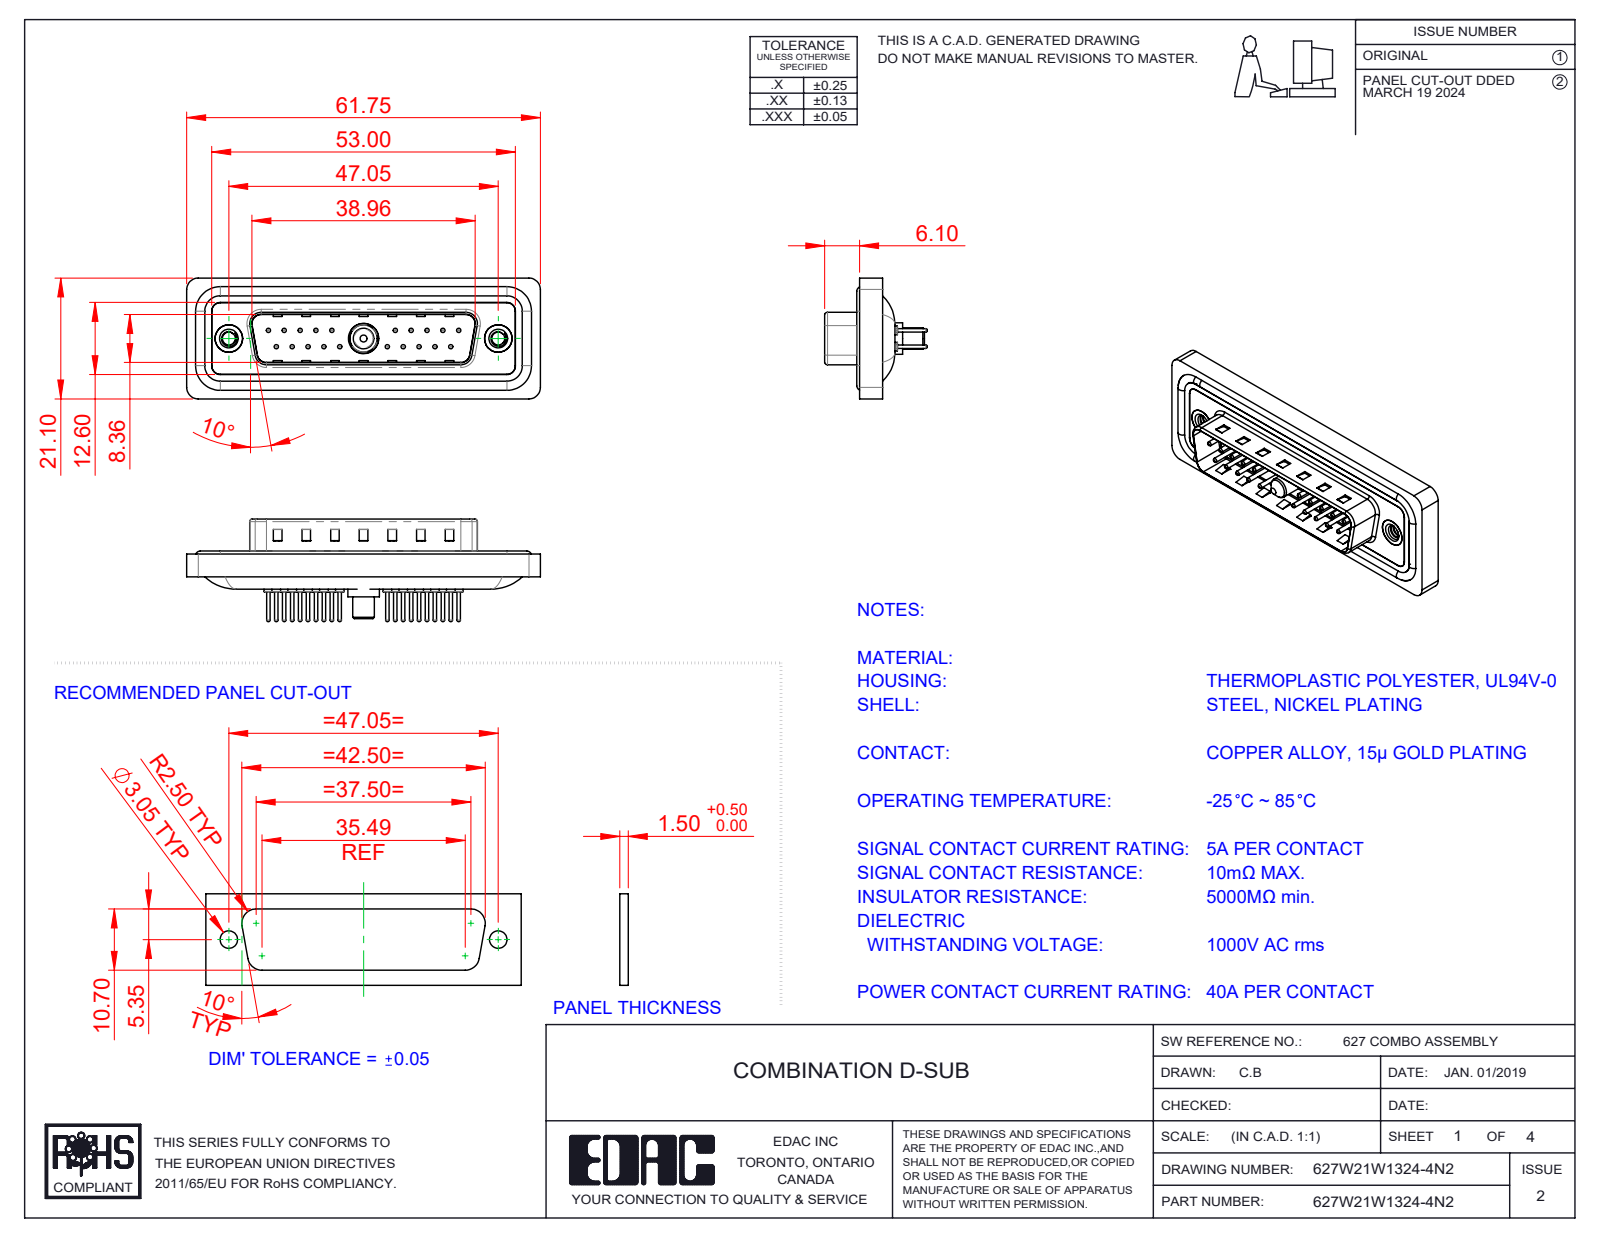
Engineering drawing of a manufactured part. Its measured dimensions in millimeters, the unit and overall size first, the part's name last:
Units: millimetres
Overall size (bounding box): 61.75 × 21.1 × 17.9
Round holes (diameter × count): ⌀0.75 ×20, ⌀1.6 ×20, ⌀2 ×20, ⌀2.26 ×2, ⌀4 ×2, ⌀4.8 ×2, ⌀5 ×2, ⌀4.85 ×1, ⌀5.3 ×1
Round bosses / shafts (diameter × count): ⌀1.5 ×20, ⌀0.6 ×20, ⌀1.6 ×4, ⌀4.9 ×2, ⌀5.5 ×1, ⌀5.2 ×1, ⌀4.75 ×1, ⌀3.75 ×1
Partial cylindrical surfaces — rounded edges, fillets, slot ends (radius × count): R1.5 ×22, R2 ×18, R0.5 ×8, R1.6 ×8, R0.25 ×4, R0.6 ×4, R0.65 ×4, R0.9 ×4
Main face-to-face distances: 0.4, 1.5, 1.1, 1.6, 0.5, 3.1, 2.9, 4.1, 0.82, 9.58
Hole centre spacings: 3.16, 2.77, 5.54, 8.31, 5.04, 19.39, 20.97, 22.16
Volume: 7 216 mm³ · Surface area: 11 964 mm²
Bodies: 29 solids, 1262 faces (359 planar, 487 cylindrical, 416 other)
Part name (STEP PRODUCT): 627W21W1324-4N2; 627Combo Shell Front_25 Contacts; 627Combo Threaded Rivet_2; Power Pin_40A S (+5 more)
STEP written by: SolidWorks 2023 (CONFIG_CONTROL_DESIGN)
